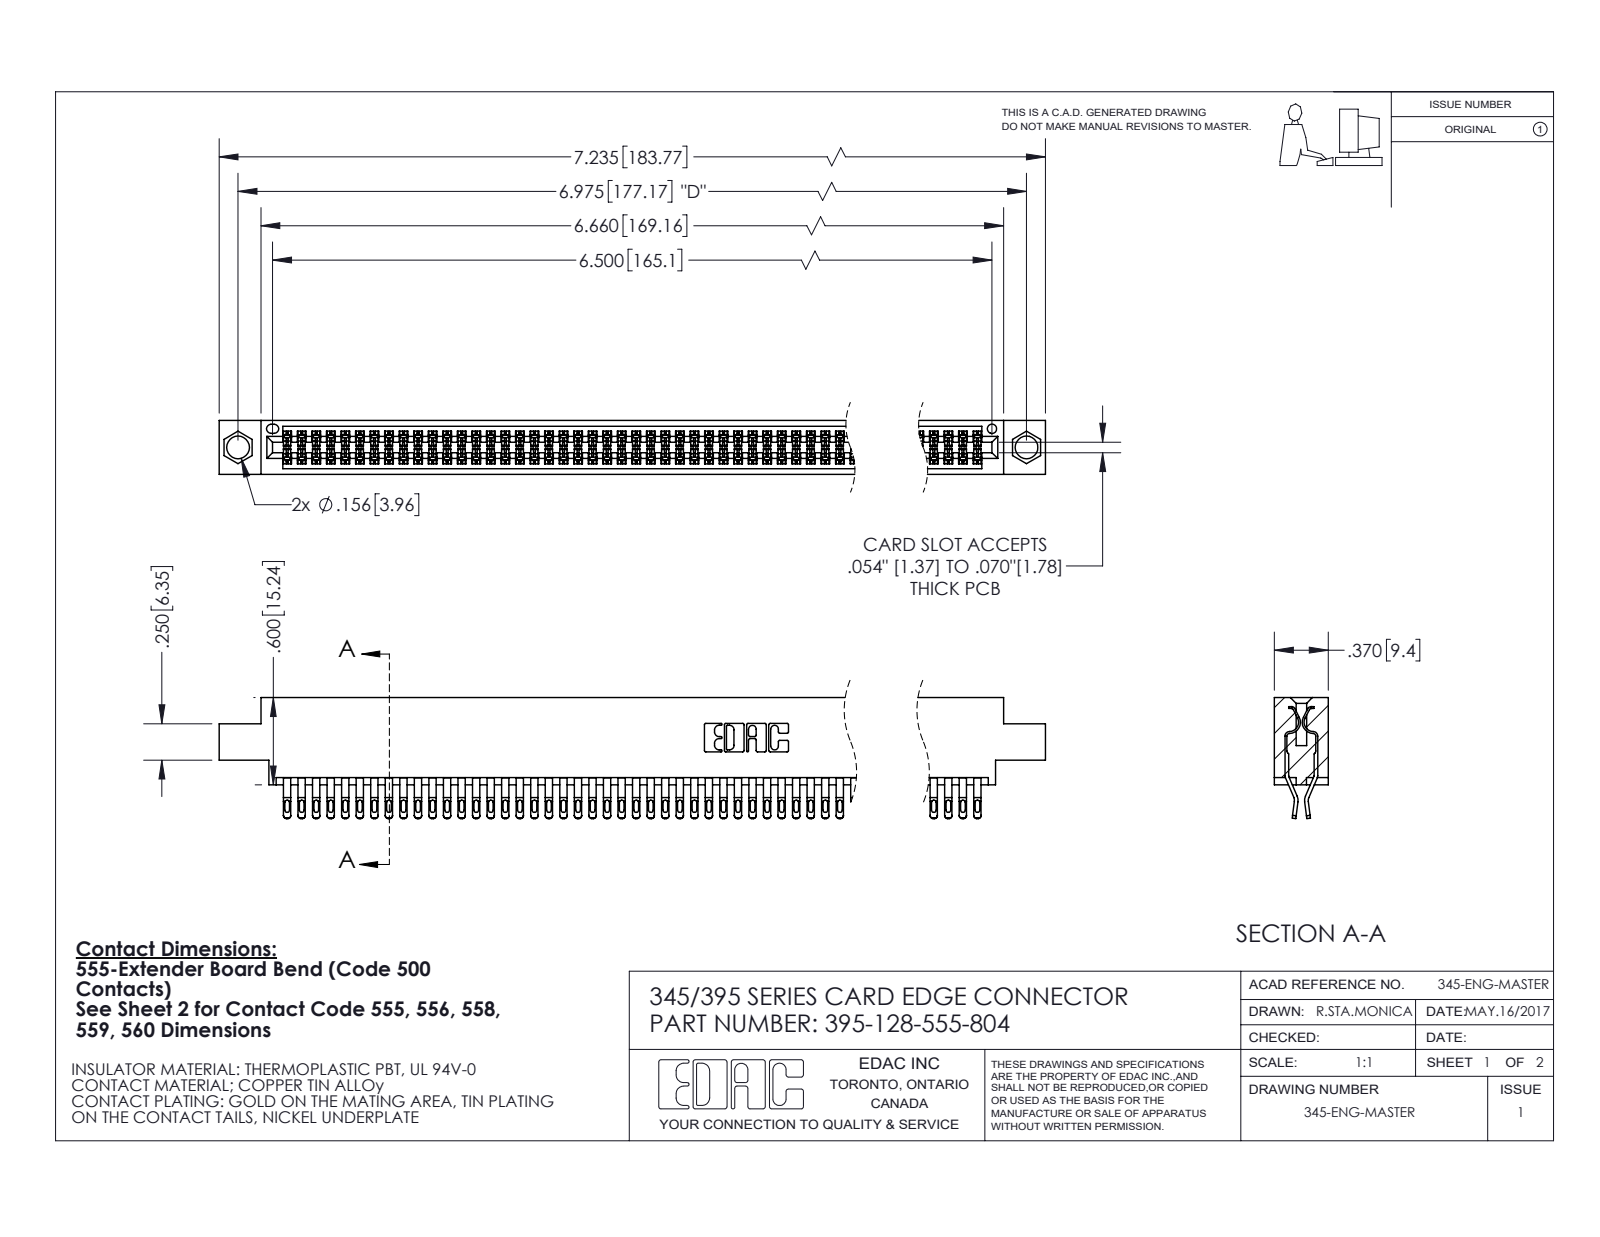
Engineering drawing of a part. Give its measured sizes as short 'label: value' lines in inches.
name: 395-128-555-804; 345-292-001_555 Tail; 345 Part_0.170 Offset - 0.156 Dia-TI
written by: SolidWorks 2020 (CONFIG_CONTROL_DESIGN)
unit: in
bodies: 129 solids, 7312 faces (4066 planar, 3246 cylindrical, 0 other)
size: 7.235 × 0.832 × 0.37
volume: 1.111 in³; area: 44.37 in²
holes: 2× ⌀0.156, 1× ⌀0.064
rounds: 320× R0.016, 256× R0.006, 256× R0.02, 22× R0.01, 6× R0.007, 6× R0.031, 3× R0.026, 2× R0.01
face distances: 0.072, 0.298, 0.025, 0.37, 0.2, 0.098, 0.272, 0.225, 0.175, 0.149
hole spacings: 0.27, 6.739, 6.975
